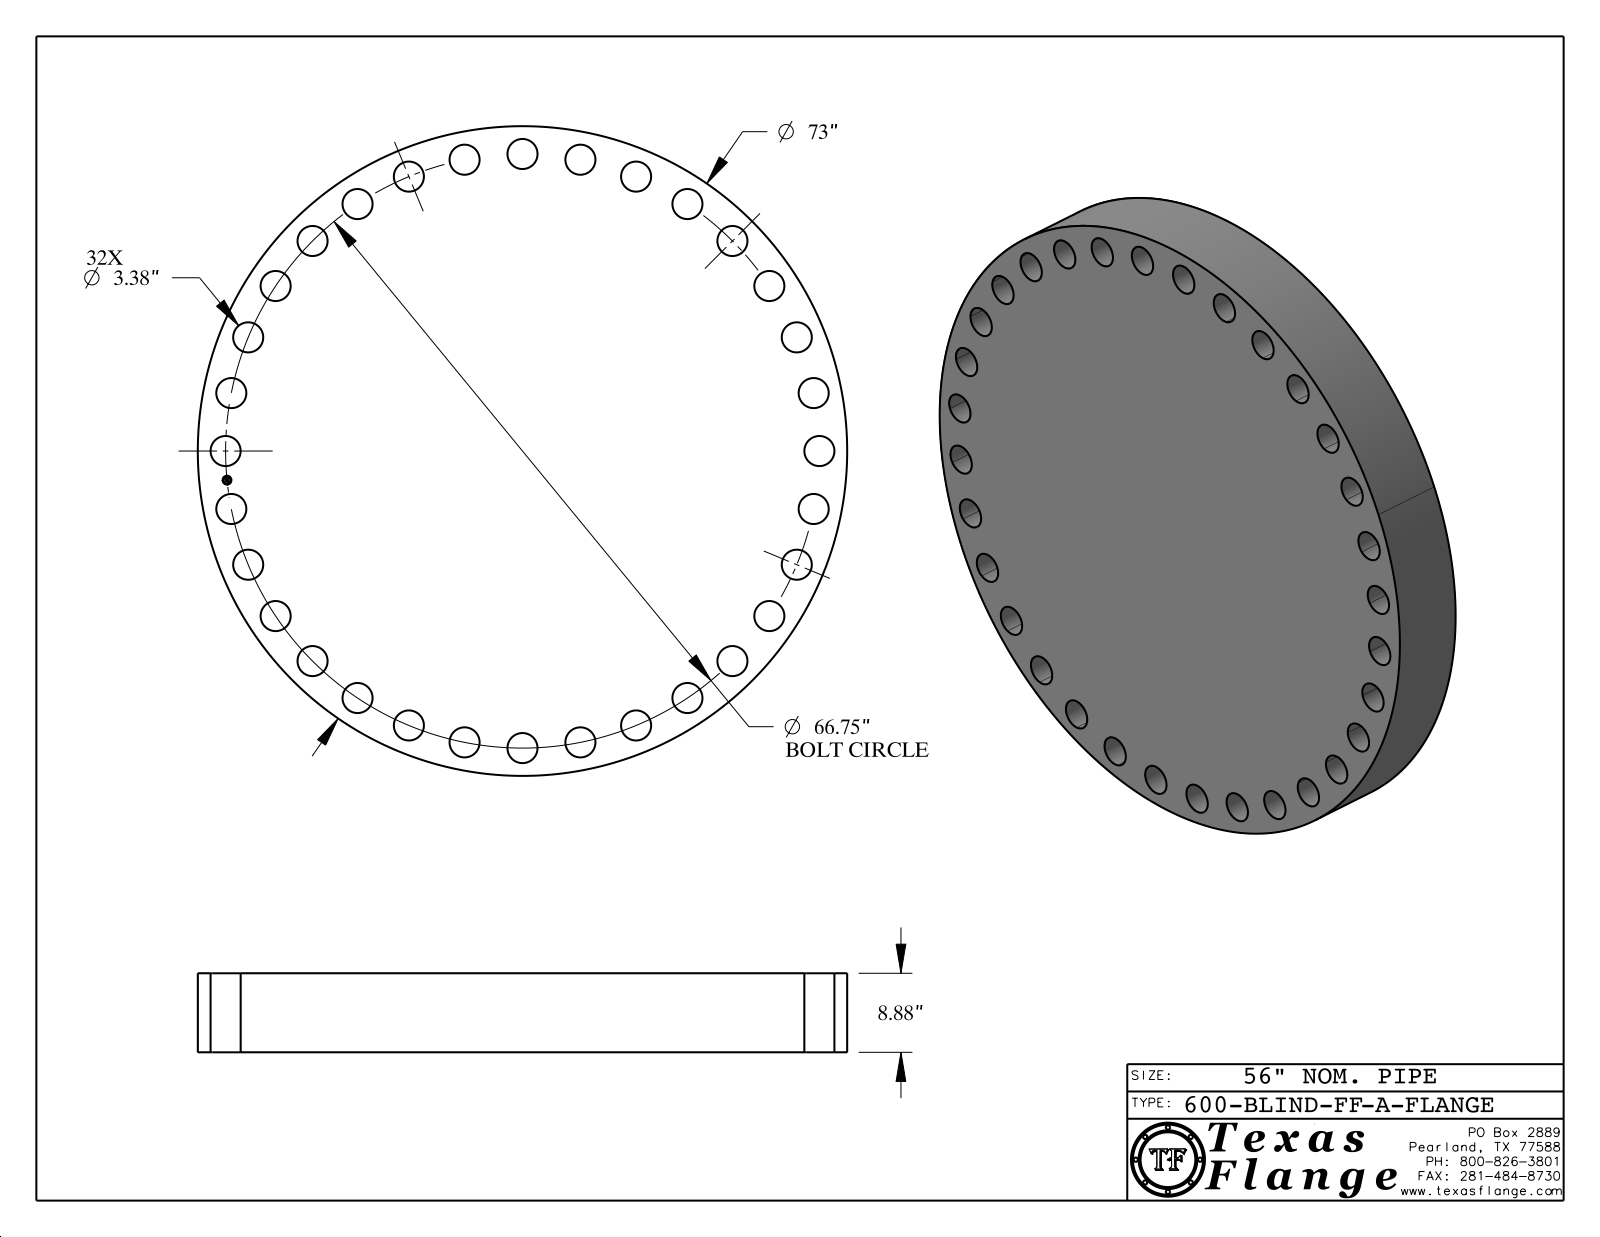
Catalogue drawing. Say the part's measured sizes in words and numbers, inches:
The part is named "600-BLIND-FF, Series A". Its 3-D file was written by "CATIA V5 STEP AP214 (AUTOMOTIVE_DESIGN)". It is 1 solid with 453 faces: 367 planar, 86 cylindrical and 0 other. Overall it measures 73 by 73 by 8.88 inches. Its volume is 34 617 cubic inches and its surface area 12 851 square inches. Round holes: 32 of diameter 3.38, 1 of diameter 1. Round bosses or shafts: 8 of diameter 0.061, 1 of diameter 73, 1 of diameter 0.788. The main face-to-face distances are 8.88, 0.015, 8.865, 0.298, 0.292, 0.054, 0.193, 0.248, 0.044, 0.15. The hole center spacings are 55.501, 58.869, 13.022, 47.2, 31.466, 51.598, 63.876, 66.429.
